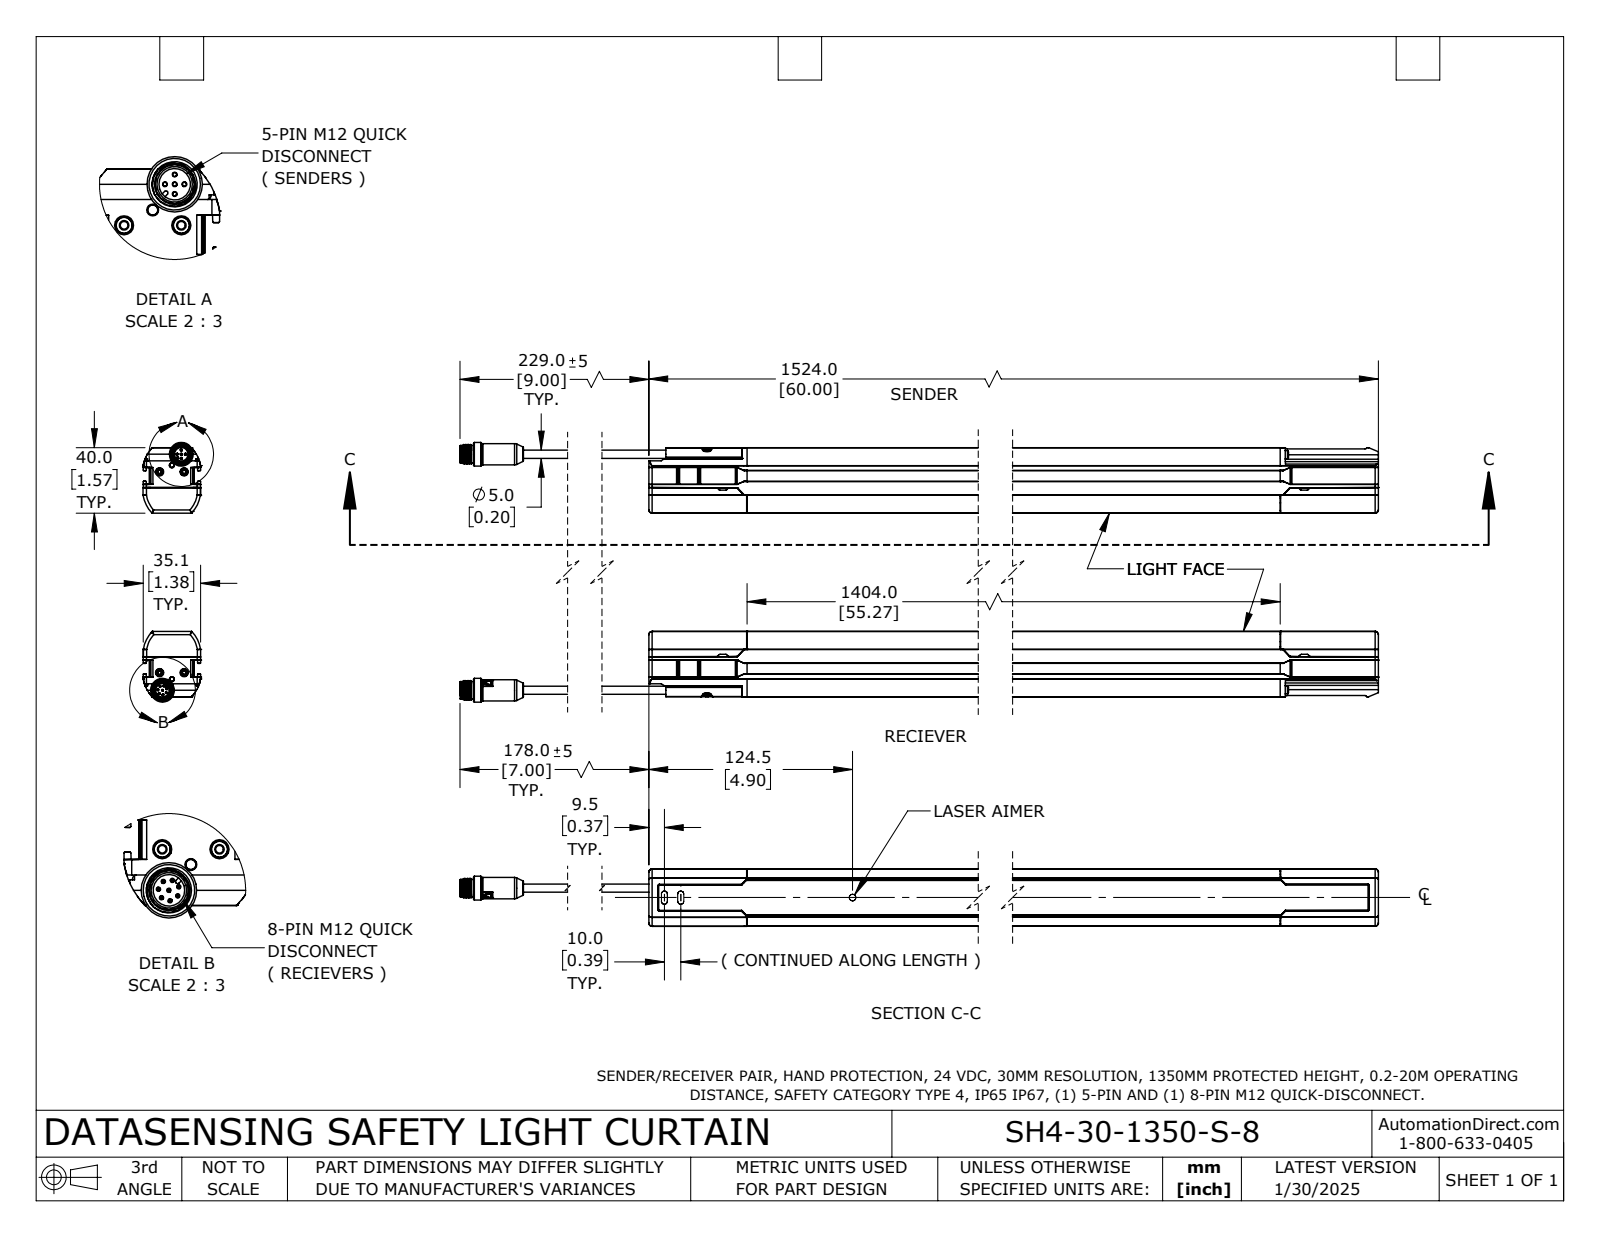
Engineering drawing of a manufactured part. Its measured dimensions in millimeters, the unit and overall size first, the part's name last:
Units: millimetres
Overall size (bounding box): 1587.3 × 158.7 × 35.2
Round holes (diameter × count): ⌀2 ×4, ⌀3 ×4, ⌀5 ×4, ⌀2.5 ×2, ⌀2.5 ×2, ⌀2.6 ×2, ⌀2.6 ×2, ⌀8.3 ×2, ⌀9.7 ×2, ⌀10.3 ×2, ⌀10.8 ×2, ⌀2.8 ×1
Round bosses / shafts (diameter × count): ⌀5 ×10, ⌀2.2 ×8, ⌀0.8 ×8, ⌀1 ×5, ⌀4.4 ×4, ⌀14.5 ×2, ⌀13 ×2, ⌀10.6 ×2
Partial cylindrical surfaces — rounded edges, fillets, slot ends (radius × count): R0.3 ×164, R0.4 ×66, R0.5 ×50, R0.2 ×36, R0.8 ×20, R0.8 ×12, R2 ×12, R1.5 ×10
Main face-to-face distances: 38, 114.2, 31, 4, 76.2, 152.2, 35, 27.1, 117.7, 1.8
Hole centre spacings: 22, 132.5, 134.3, 10.9, 15, 17.1, 122.7, 123.6
Volume: 3 212 000 mm³ · Surface area: 539 800 mm²
Bodies: 4 solids, 2608 faces (1186 planar, 784 cylindrical, 638 other)
Part name (STEP PRODUCT): SH4-30-1350-S-8
STEP written by: SolidWorks 2024 (AUTOMOTIVE_DESIGN)
